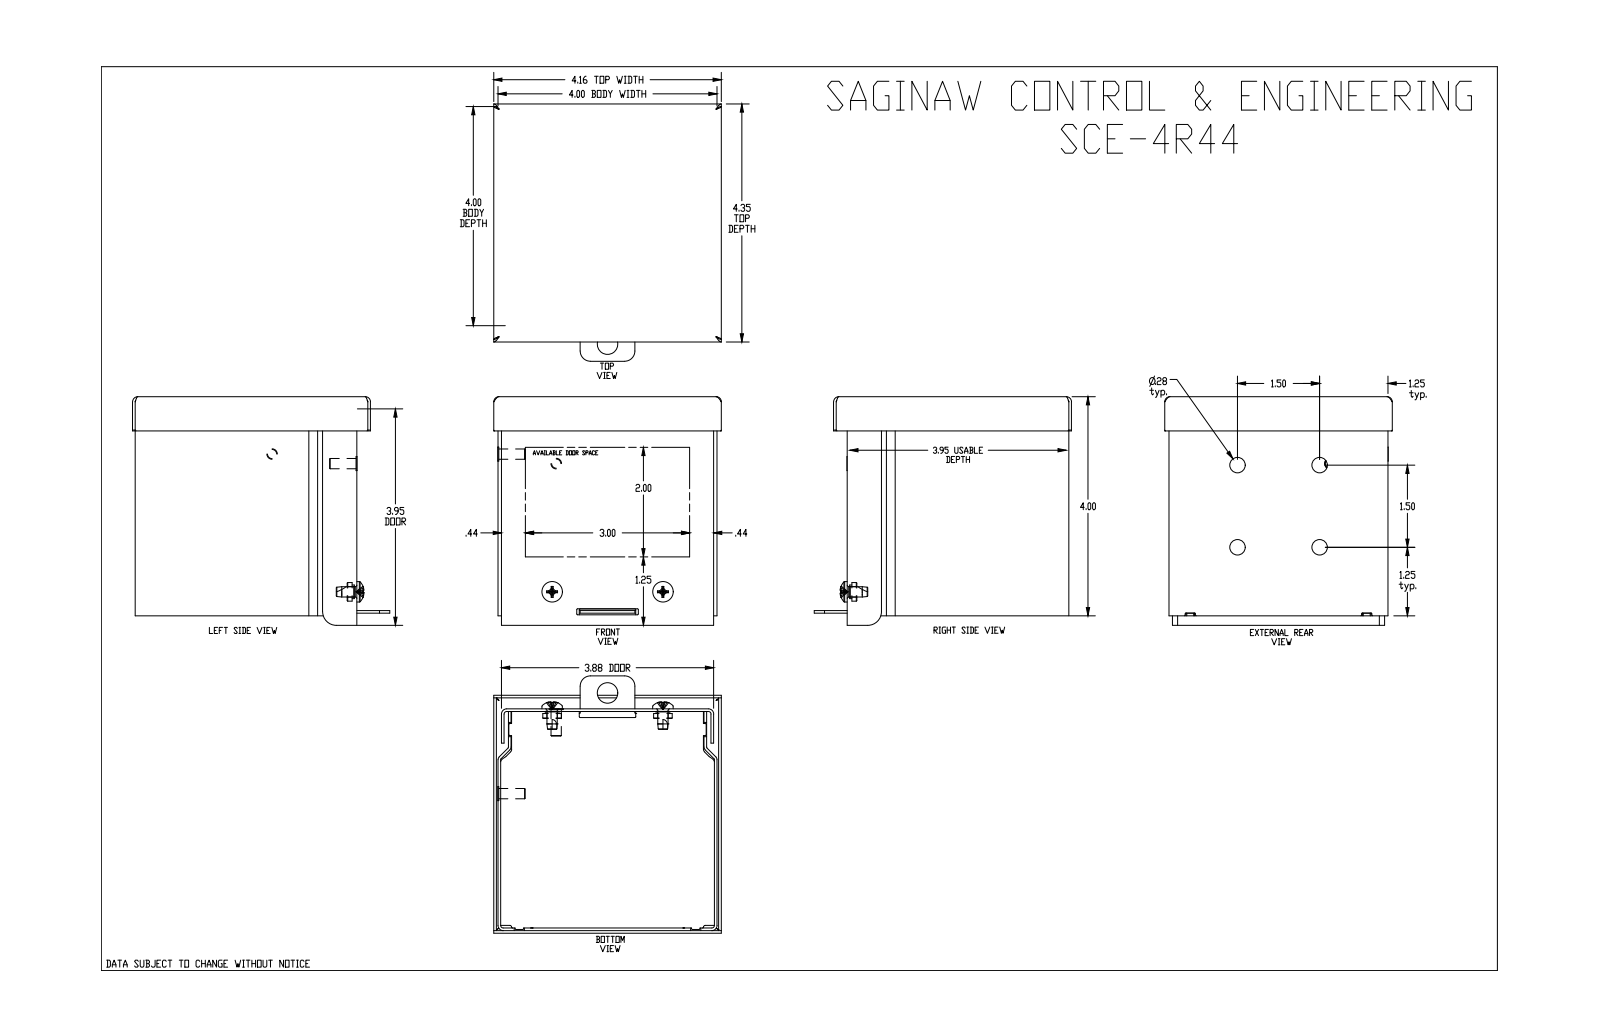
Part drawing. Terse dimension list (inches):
name: SCE-4R44
written by: SolidWorks 2021 (AUTOMOTIVE_DESIGN)
unit: in
bodies: 11 solids, 477 faces (231 planar, 164 cylindrical, 82 other)
size: 4.698 × 4.174 × 4.156
volume: 6.109 in³; area: 245.7 in²
holes: 4× ⌀0.281, 3× ⌀0.19, 2× ⌀0.25, 1× ⌀0.188, 1× ⌀0.193, 1× ⌀0.375
bosses: 4× ⌀0.188, 2× ⌀0.373, 2× ⌀0.34, 2× ⌀0.256, 2× ⌀0.249
rounds: 32× R0.015, 12× R0.125, 8× R0.047, 8× R0.06, 8× R0.095, 4× R0.025, 4× R0.062, 4× R0.073
face distances: 0.048, 3.952, 4, 0.06, 3.904, 3.892, 3.94, 4.048, 0.19, 3.762
hole spacings: 1.5, 0.854, 1.94, 2.121, 2.328, 2.907, 0.189, 1.335
